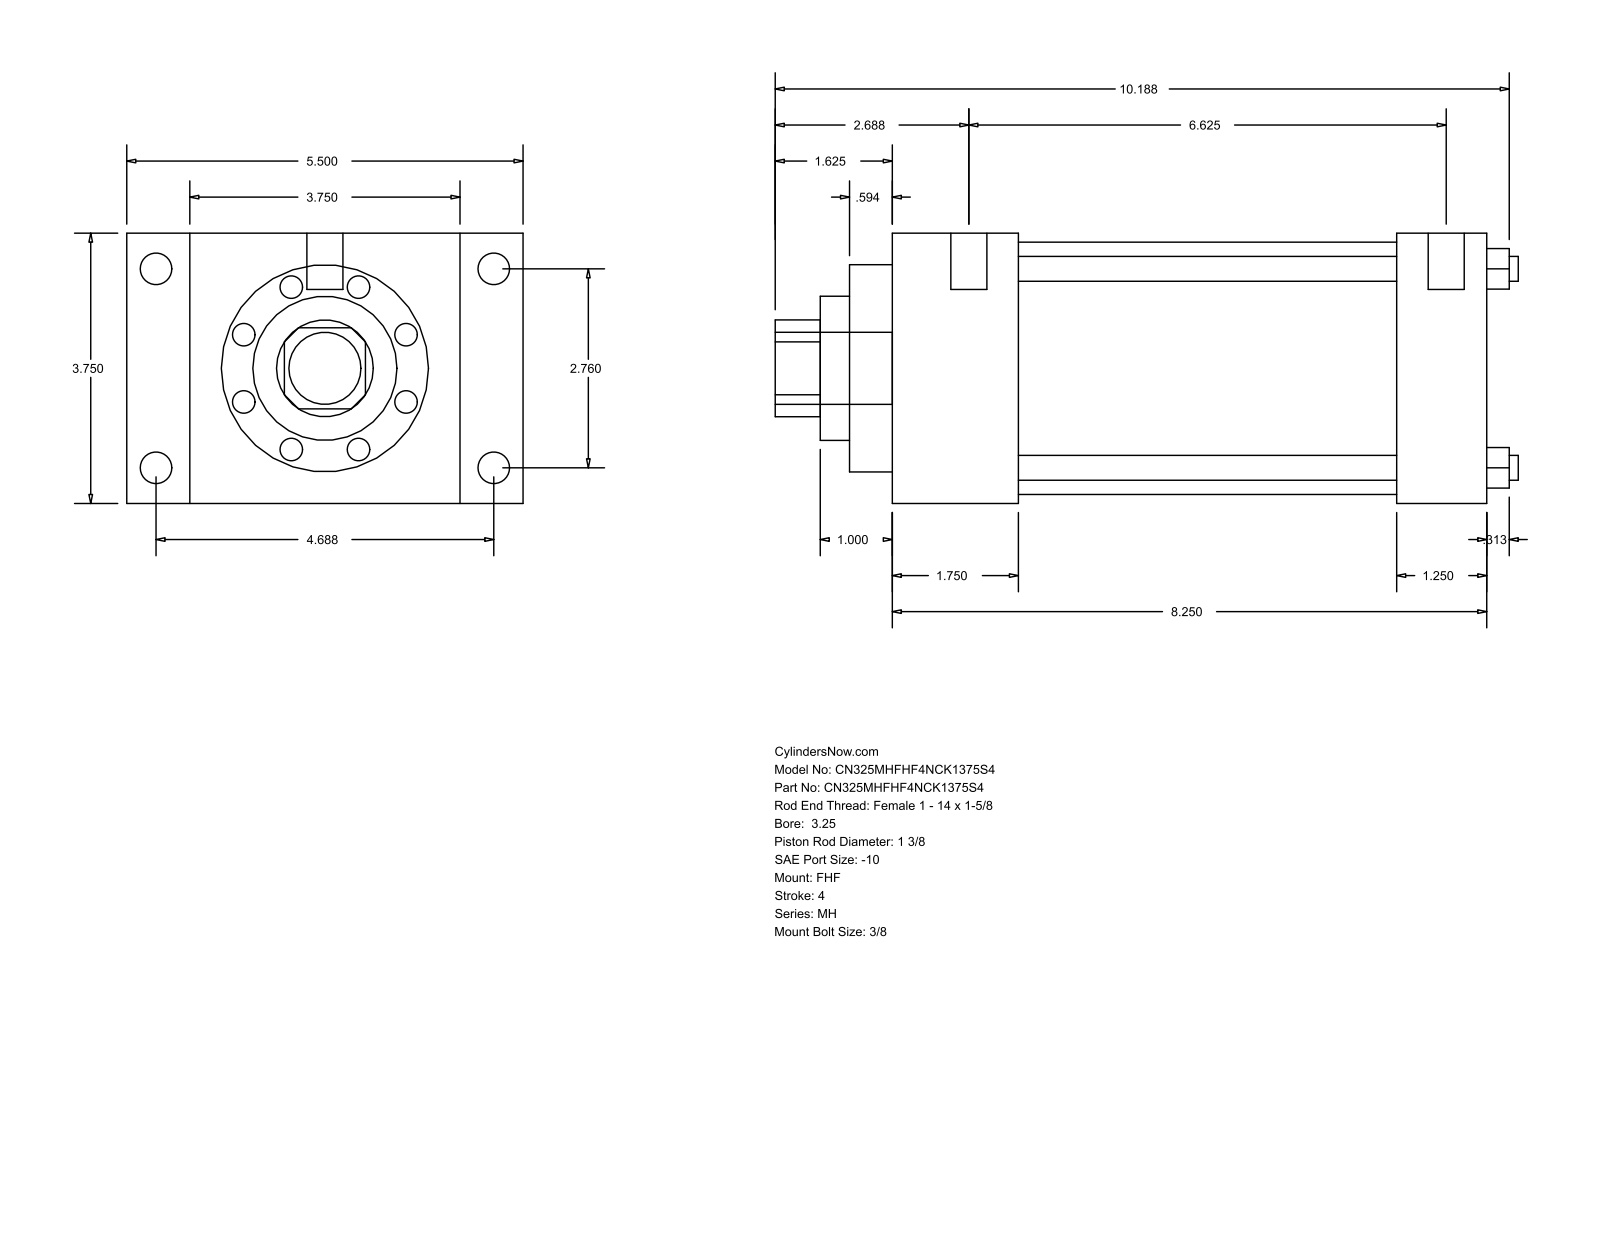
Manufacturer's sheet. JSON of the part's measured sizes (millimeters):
{"part_name": "MH_FHF__0325_1.375", "step_written_by": "GSSL Pune (CONFIG_CONTROL_DESIGN)", "units": "millimeters", "bodies": {"solids": 0, "faces": 90, "planar": 61, "cylindrical": 29, "other": 0}, "overall_size": [261.94, 139.7, 95.25], "round_holes": [[8.76, 4], [34.92, 1], [50.8, 1], [73.03, 1], [88.9, 1]], "round_bosses_or_shafts": [[11.13, 4], [5.56, 4], [12.7, 2], [25.4, 1]], "partial_cylinders_radius": [[17.06, 1]], "face_to_face_distances": [95.24, 209.55, 44.45, 165.1, 22.23, 117.47, 139.7, 177.8, 133.35, 31.75], "hole_center_spacings": [49.57, 70.1, 99.14]}
